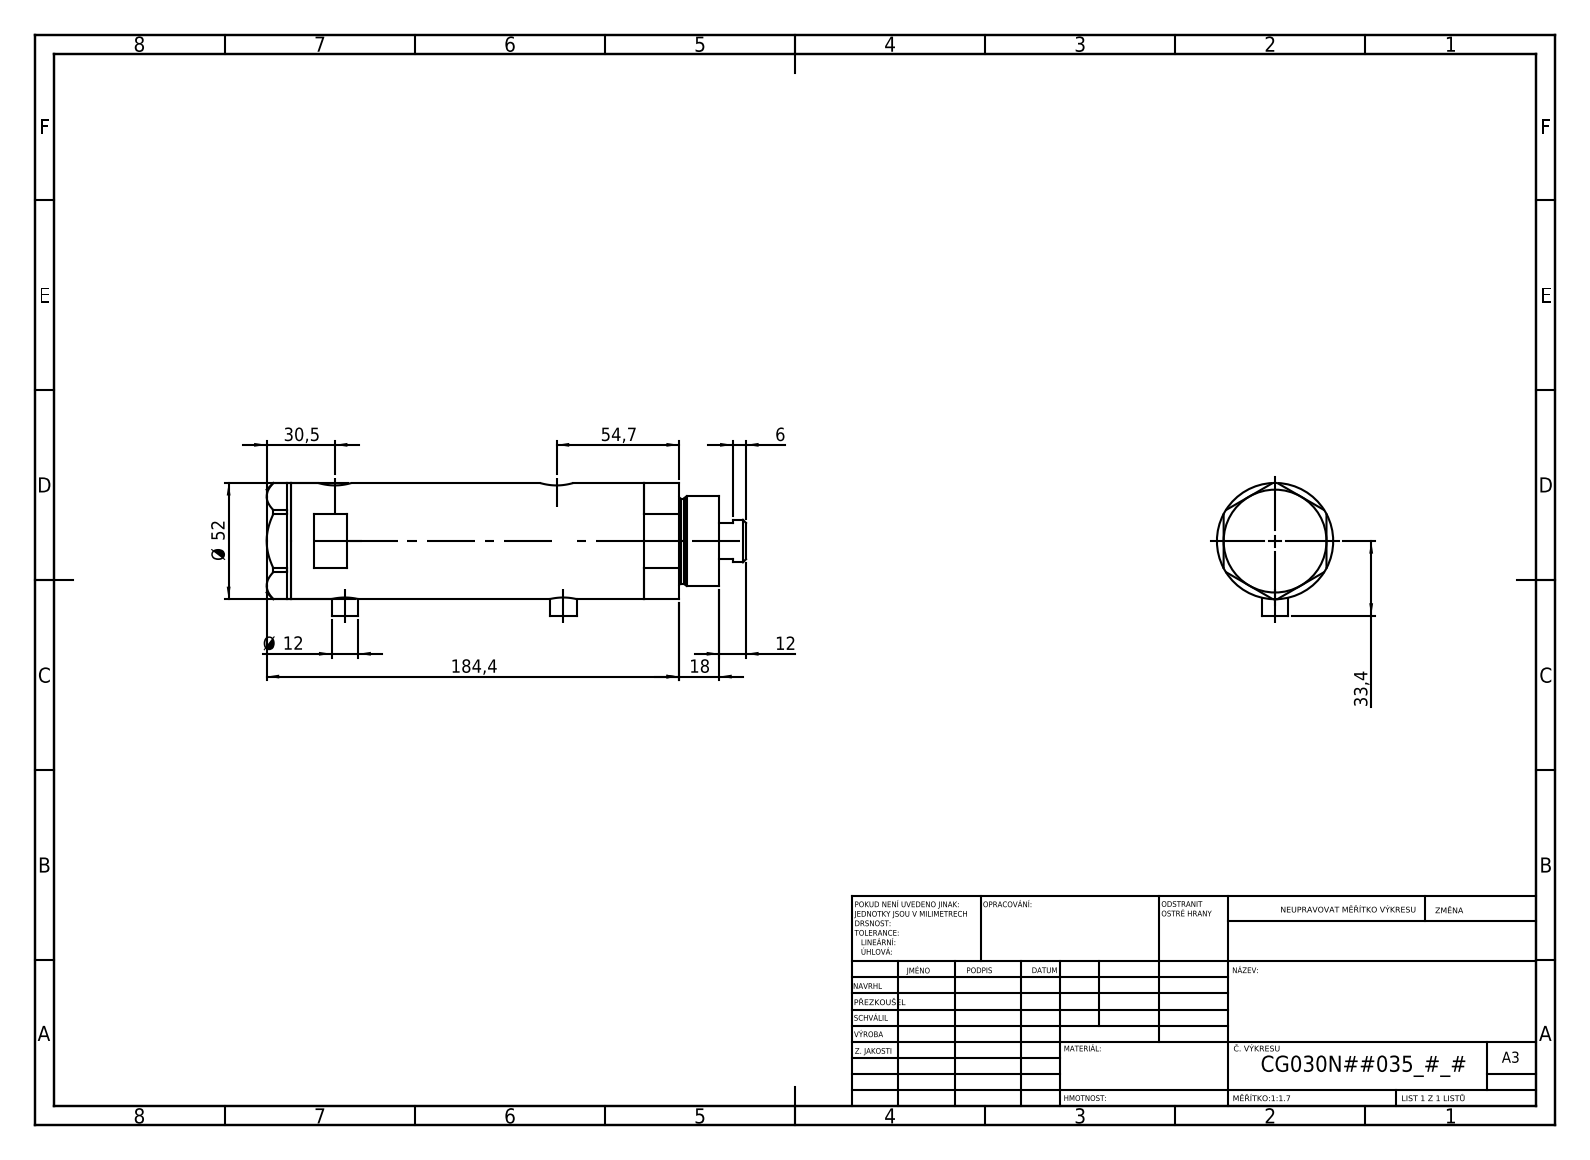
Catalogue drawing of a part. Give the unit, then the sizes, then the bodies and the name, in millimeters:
Units: millimetres
Overall size (bounding box): 214.4 × 59.4 × 52
Round holes (diameter × count): ⌀9.73 ×2, ⌀12.5 ×2, ⌀15 ×2, ⌀6.5 ×1, ⌀20 ×1, ⌀21.5 ×1, ⌀30 ×1, ⌀33 ×1, ⌀44 ×1
Round bosses / shafts (diameter × count): ⌀12 ×2, ⌀52 ×1, ⌀40 ×1, ⌀38 ×1, ⌀19 ×1
Main face-to-face distances: 121.5, 23.8, 97.7, 11, 34.8, 132.5, 46, 168.9, 157.9, 134.1
Hole centre spacings: 2.9, 4.5, 94.7, 97.6, 99.2, 102.1
Volume: 396 668 mm³ · Surface area: 87 533 mm²
Bodies: 4 solids, 134 faces (65 planar, 49 cylindrical, 20 other)
Part name (STEP PRODUCT): V270CG_FRONT; V270CG_MIDDLE; V270CG_BACK; V270CG_VC
STEP written by: SolidWorks 2019 (CONFIG_CONTROL_DESIGN)
